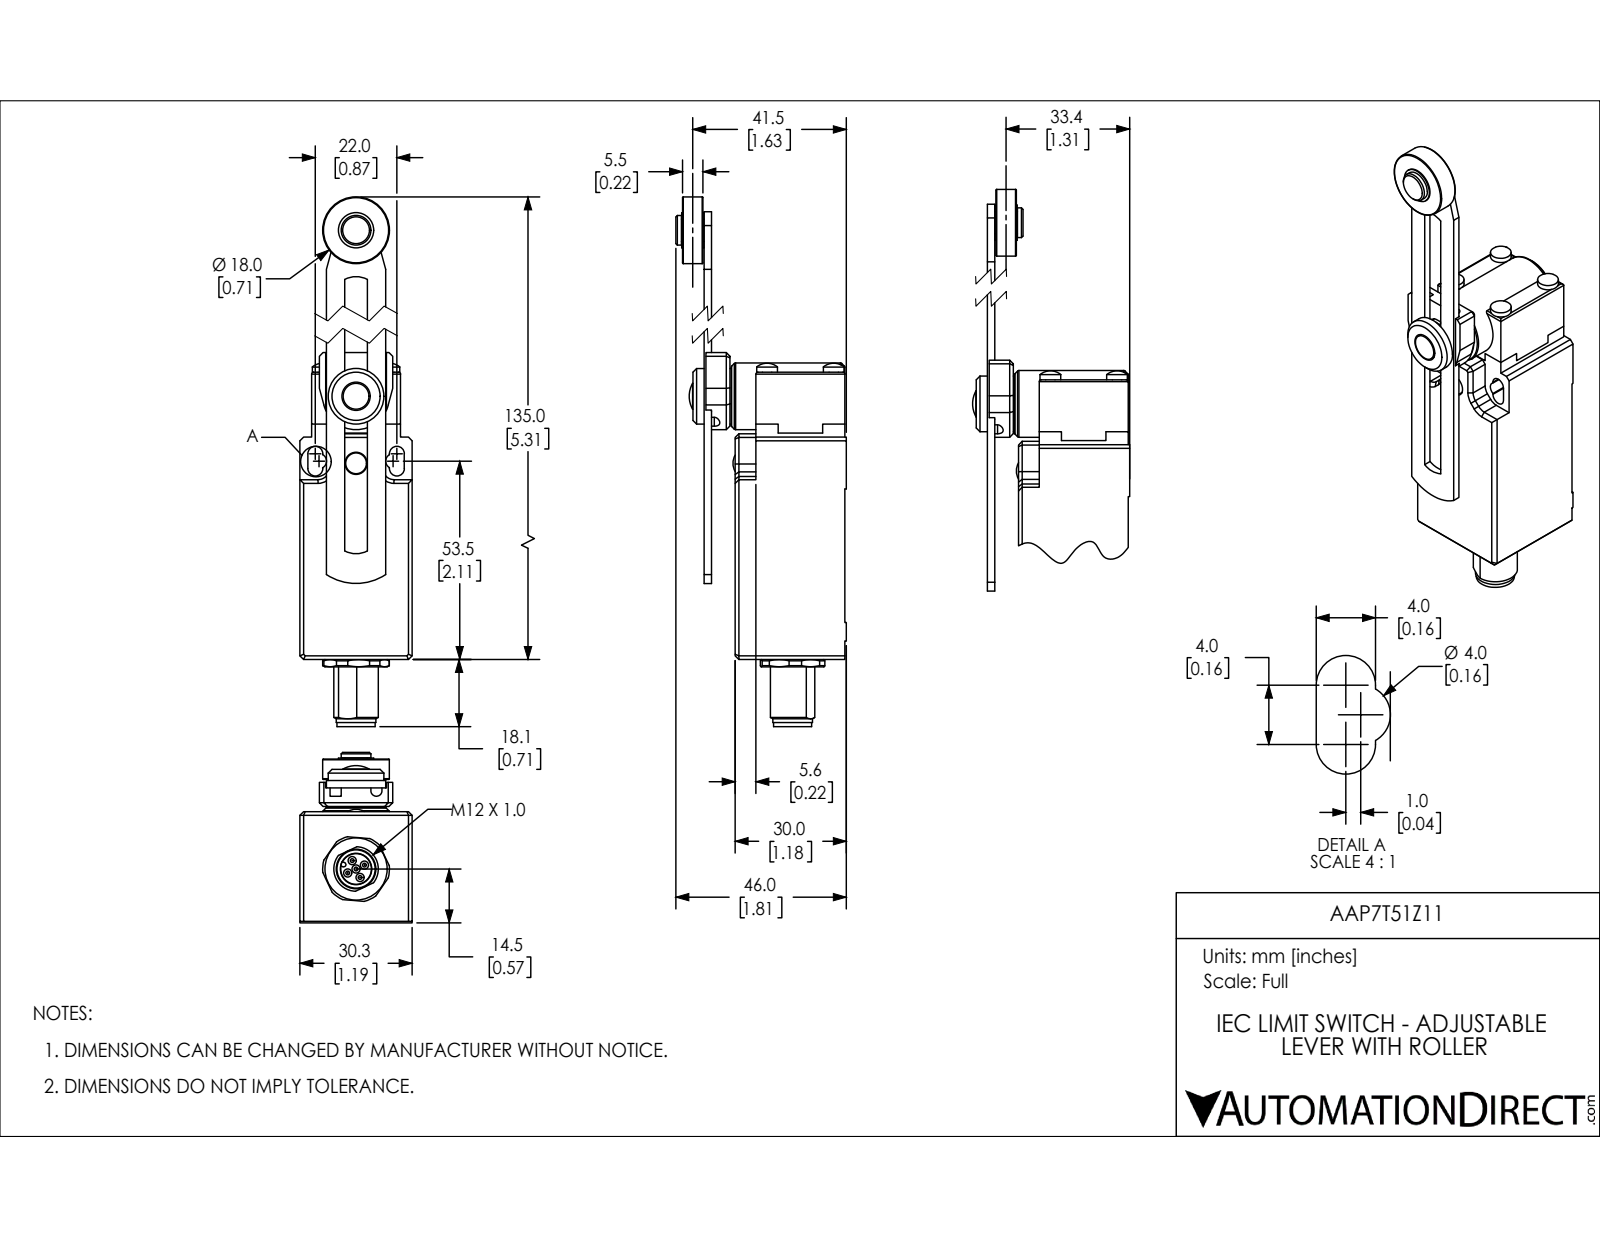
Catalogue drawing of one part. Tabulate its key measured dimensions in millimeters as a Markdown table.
| quantity | value |
| --- | --- |
| part name | AAP7T51Z11 |
| STEP written by | SolidWorks 2018 (AUTOMOTIVE_DESIGN) |
| units | millimeters |
| bodies | 6 solids, 405 faces (196 planar, 143 cylindrical, 66 other) |
| overall size | 153.1 × 46 × 30.3 |
| volume | 72 070 mm³ |
| surface area | 22 100 mm² |
| round holes (diameter × count) | 2.2 × 5, 6 × 1, 7.6 × 1, 11 × 1, 13 × 1, 14 × 1, 16 × 1 |
| round bosses / shafts (diameter × count) | 5.6 × 5, 1.4 × 5, 1 × 5, 18 × 2, 15 × 1, 10.7 × 1, 10.3 × 1, 9.5 × 1 |
| partial cylindrical surfaces (radius × count) | 2 × 6, 0.5 × 4, 3 × 4, 6.5 × 2, 0.6 × 1, 1.5 × 1, 4.6 × 1, 5 × 1 |
| main face-to-face distances | 2, 30.3, 29.6, 6.4, 36, 38, 8.4, 7, 3.1, 27.2 |
| hole center spacings | 2.5, 3.5, 5, 18.1 |
